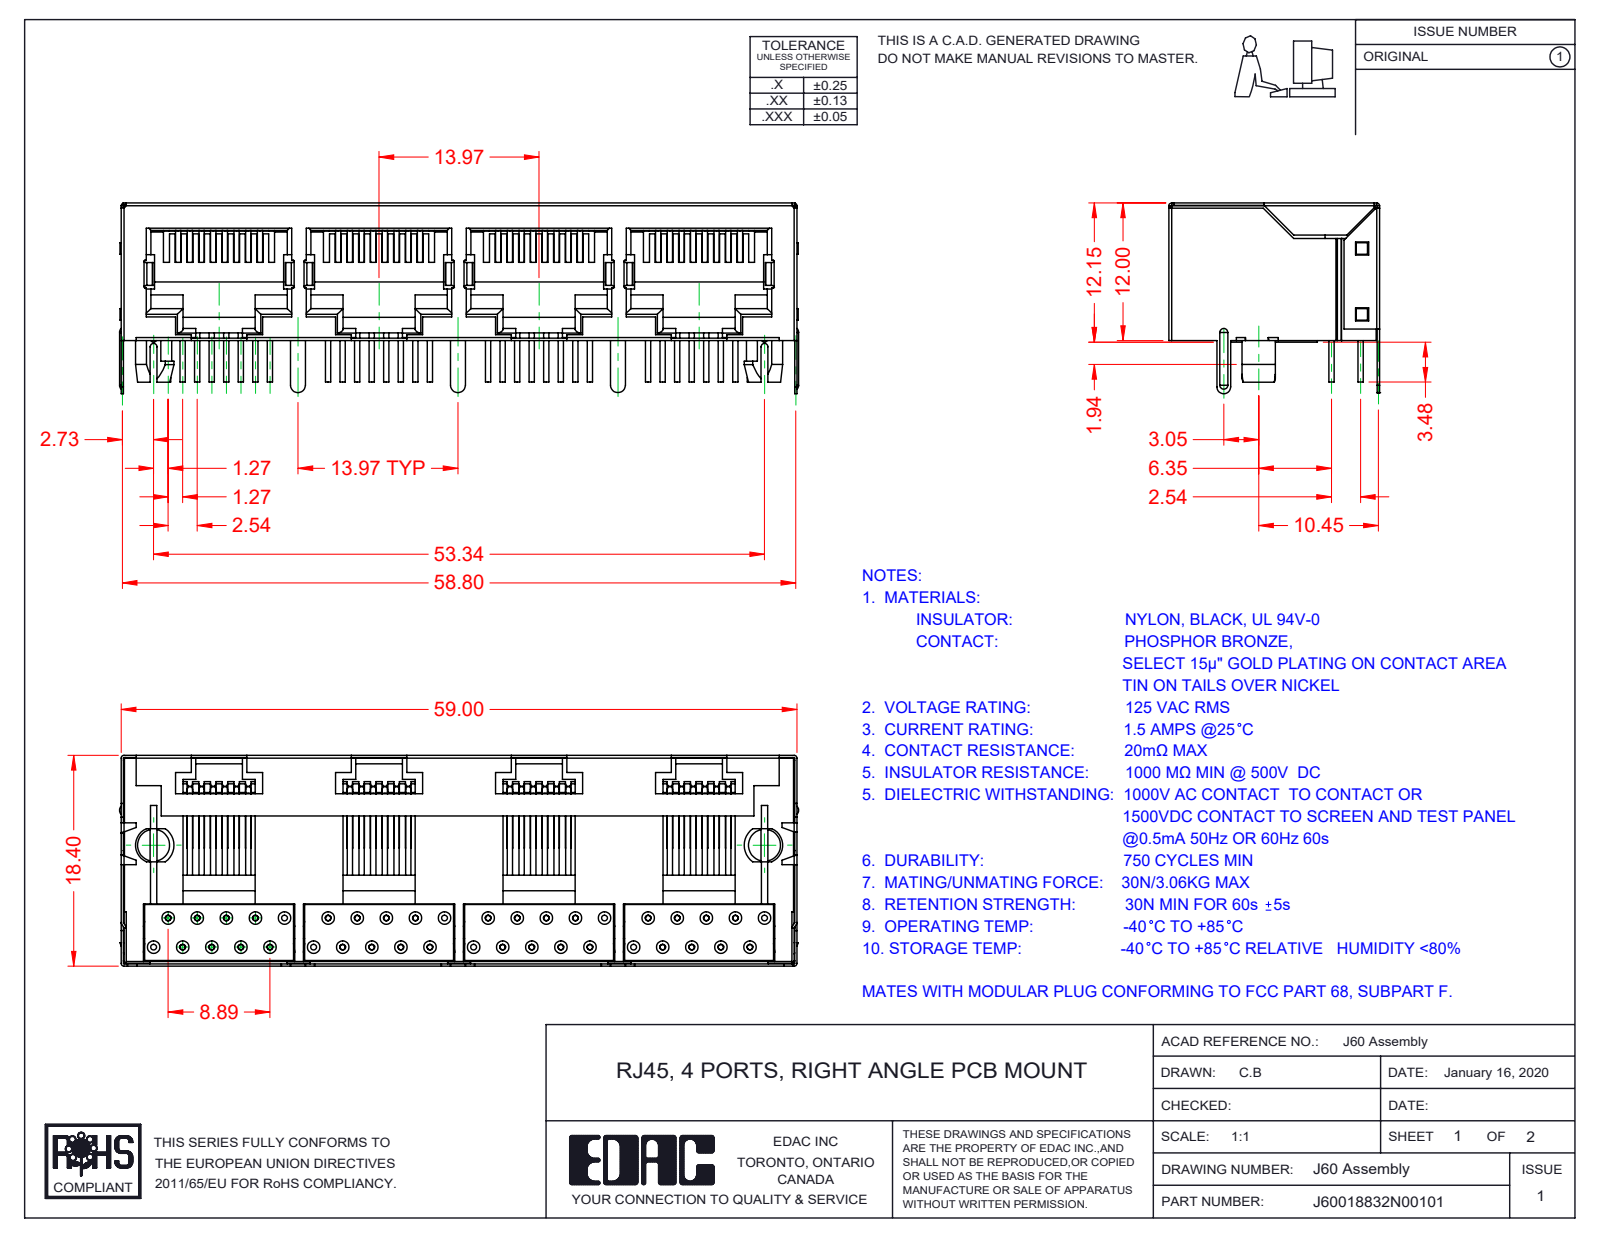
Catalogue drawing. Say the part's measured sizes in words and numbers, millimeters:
The part is named "60 Contacts_8P8C; 60 Shield; RJ60048832N00101; 60 Insulator". Its 3-D file was written by "SolidWorks 2016 (CONFIG_CONTROL_DESIGN)". It is 34 solids with 2562 faces: 1489 planar, 715 cylindrical and 358 other. Overall it measures 59.3 by 18.4 by 16.65 millimeters. Its volume is 7 013 cubic millimeters and its surface area 18 560 square millimeters. Round holes: 40 of diameter 0.5, 40 of diameter 1.1. Round bosses or shafts: 96 of diameter 0.46. Partial cylindrical surfaces (rounded edges, fillets, slot ends): 26 of radius 0.3, 21 of radius 0.25, 18 of radius 0.5, 16 of radius 0.1, 10 of radius 0.21, 7 of radius 0.8, 3 of radius 0.65, 2 of radius 0.28. The main face-to-face distances are 0.5, 11.75, 11.55, 13.97, 2.19, 5.38, 5.18, 4.88, 18.2, 11.5. The hole center spacings are 2.84, 2.54, 4.58, 13.97, 5.08, 12.95, 15.45, 11.43.
